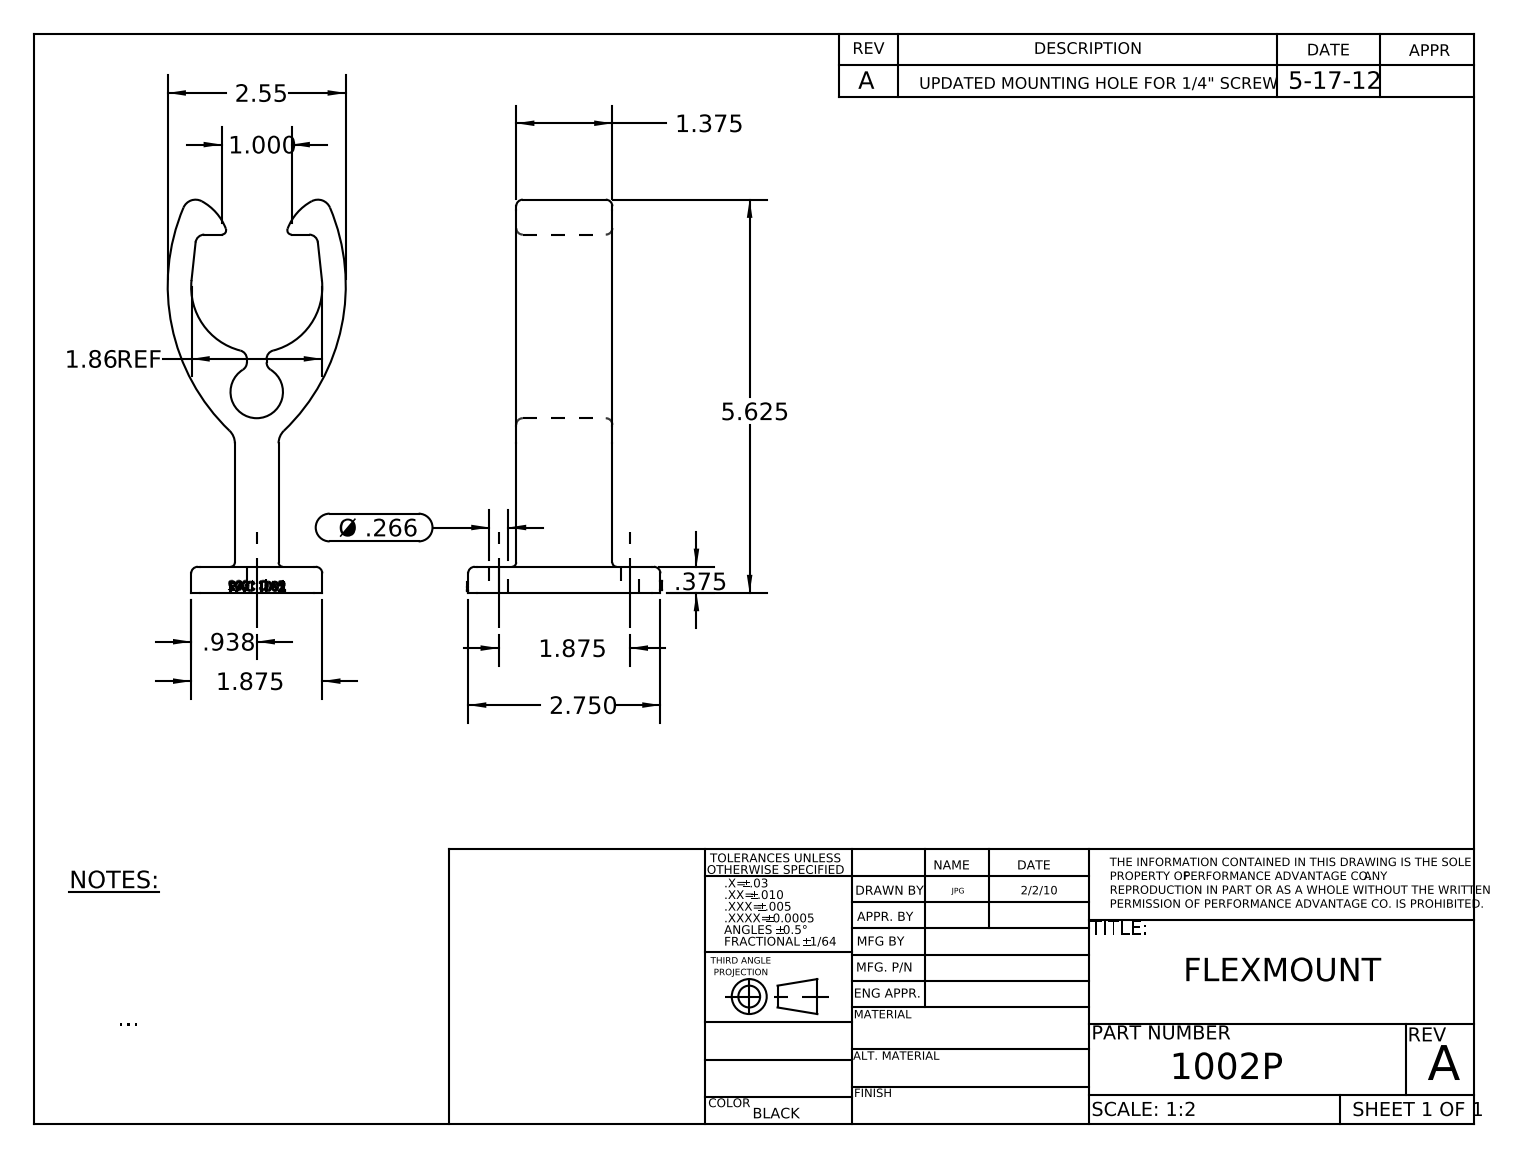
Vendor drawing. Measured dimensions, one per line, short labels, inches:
name: 1002P
written by: SolidWorks 2014 (CONFIG_CONTROL_DESIGN)
unit: in
bodies: 1 solid, 292 faces (104 planar, 56 cylindrical, 132 other)
size: 5.625 × 2.781 × 2.546
volume: 7.958 in³; area: 47.76 in²
holes: 2× ⌀0.266, 1× ⌀0.75
rounds: 18× R0.094, 10× R0.125, 4× R0.063, 2× R0.062, 2× R0.188, 2× R0.25, 2× R0.75, 2× R2.875
face distances: 0.375, 1.375, 0.625, 0.625, 1.25, 0.687, 2.062, 1.875, 5.125, 4.75
hole spacings: 1.875
